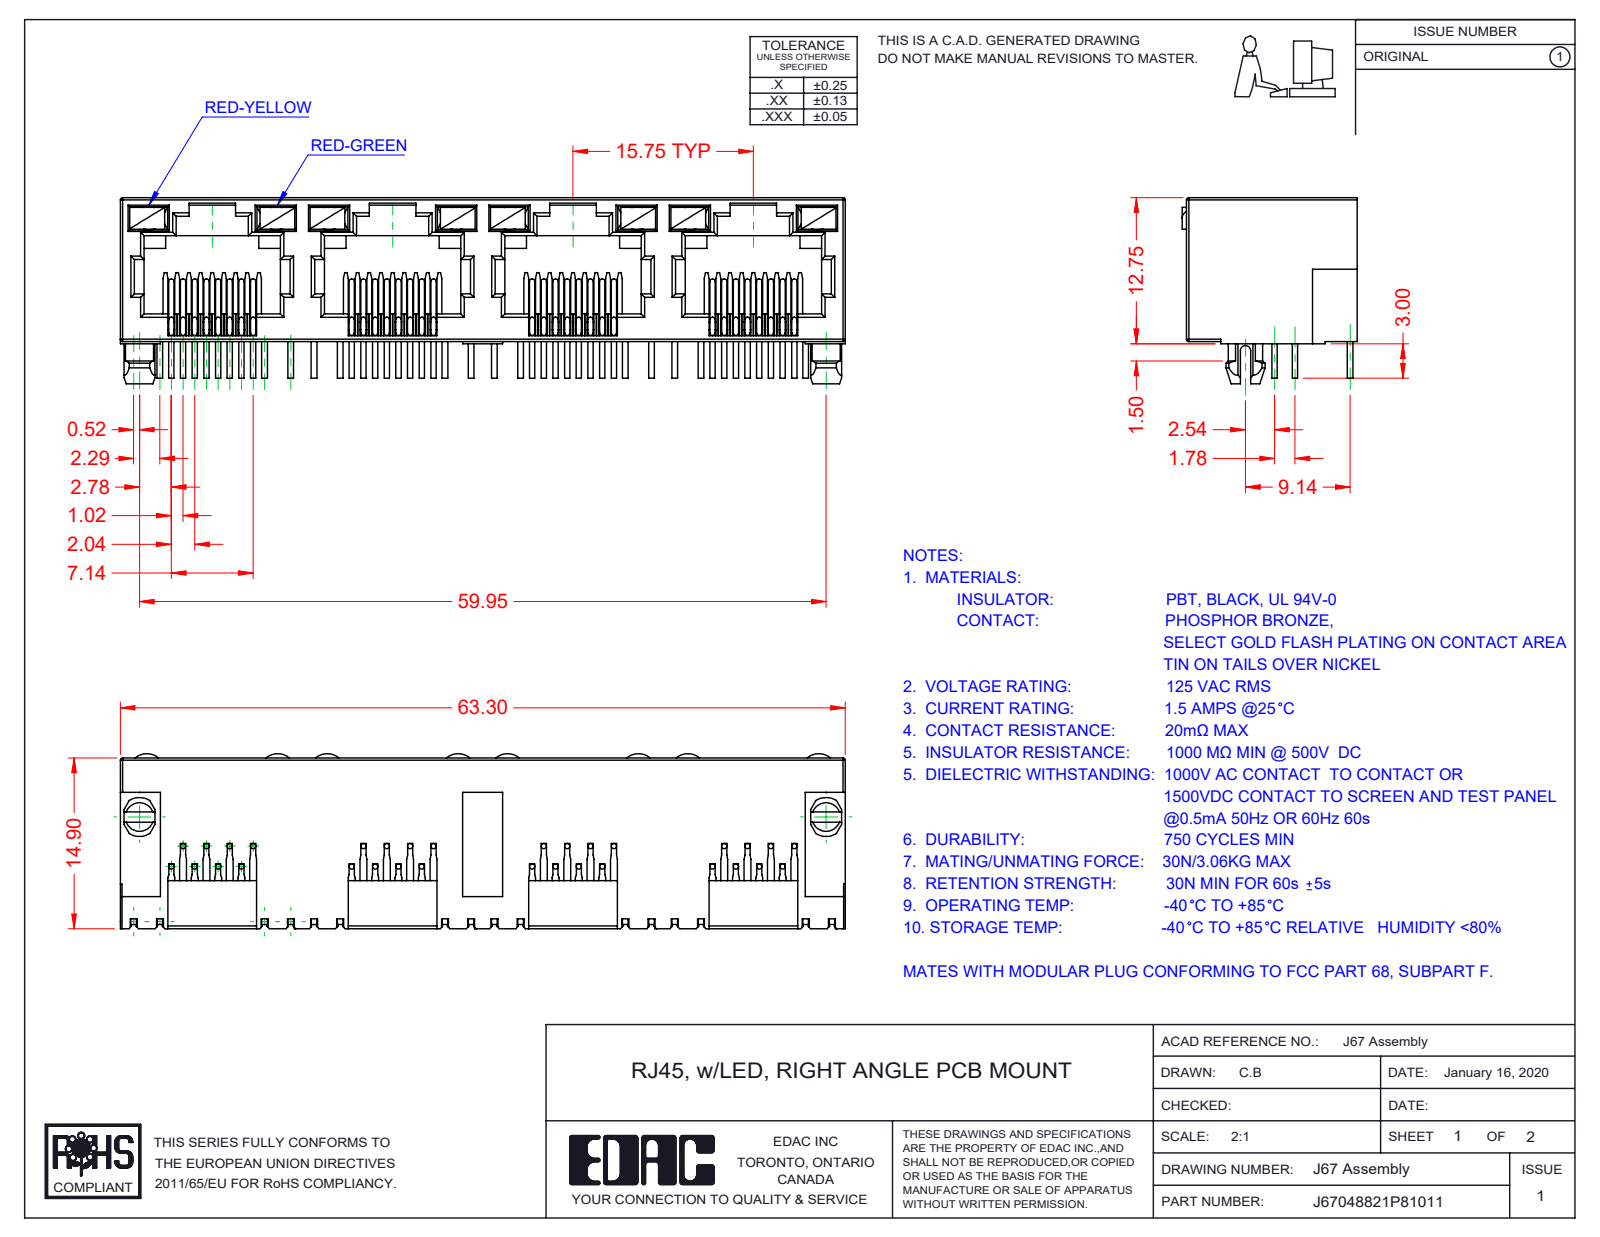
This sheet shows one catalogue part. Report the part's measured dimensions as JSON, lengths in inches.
{"part_name": "J67048822P86011; 67 LED LH_8-Red-Yellow; 67 Insulator; 67 LED RH_6-Red-Green (+1 more)", "step_written_by": "SolidWorks 2016 (CONFIG_CONTROL_DESIGN)", "units": "inches", "bodies": {"solids": 41, "faces": 2481, "planar": 1781, "cylindrical": 492, "other": 208}, "overall_size": [2.492, 0.64, 0.602], "volume_in3": 0.315, "surface_area_in2": 17.94, "round_bosses_or_shafts": [[0.018, 96]], "partial_cylinders_radius": [[0.008, 66], [0.012, 29], [0.018, 9], [0.061, 8], [0.059, 2], [0.067, 2], [0.014, 1], [0.039, 1]], "face_to_face_distances": [0.02, 0.494, 0.074, 0.035, 0.394, 0.62, 0.039, 0.055, 0.433, 0.468]}
